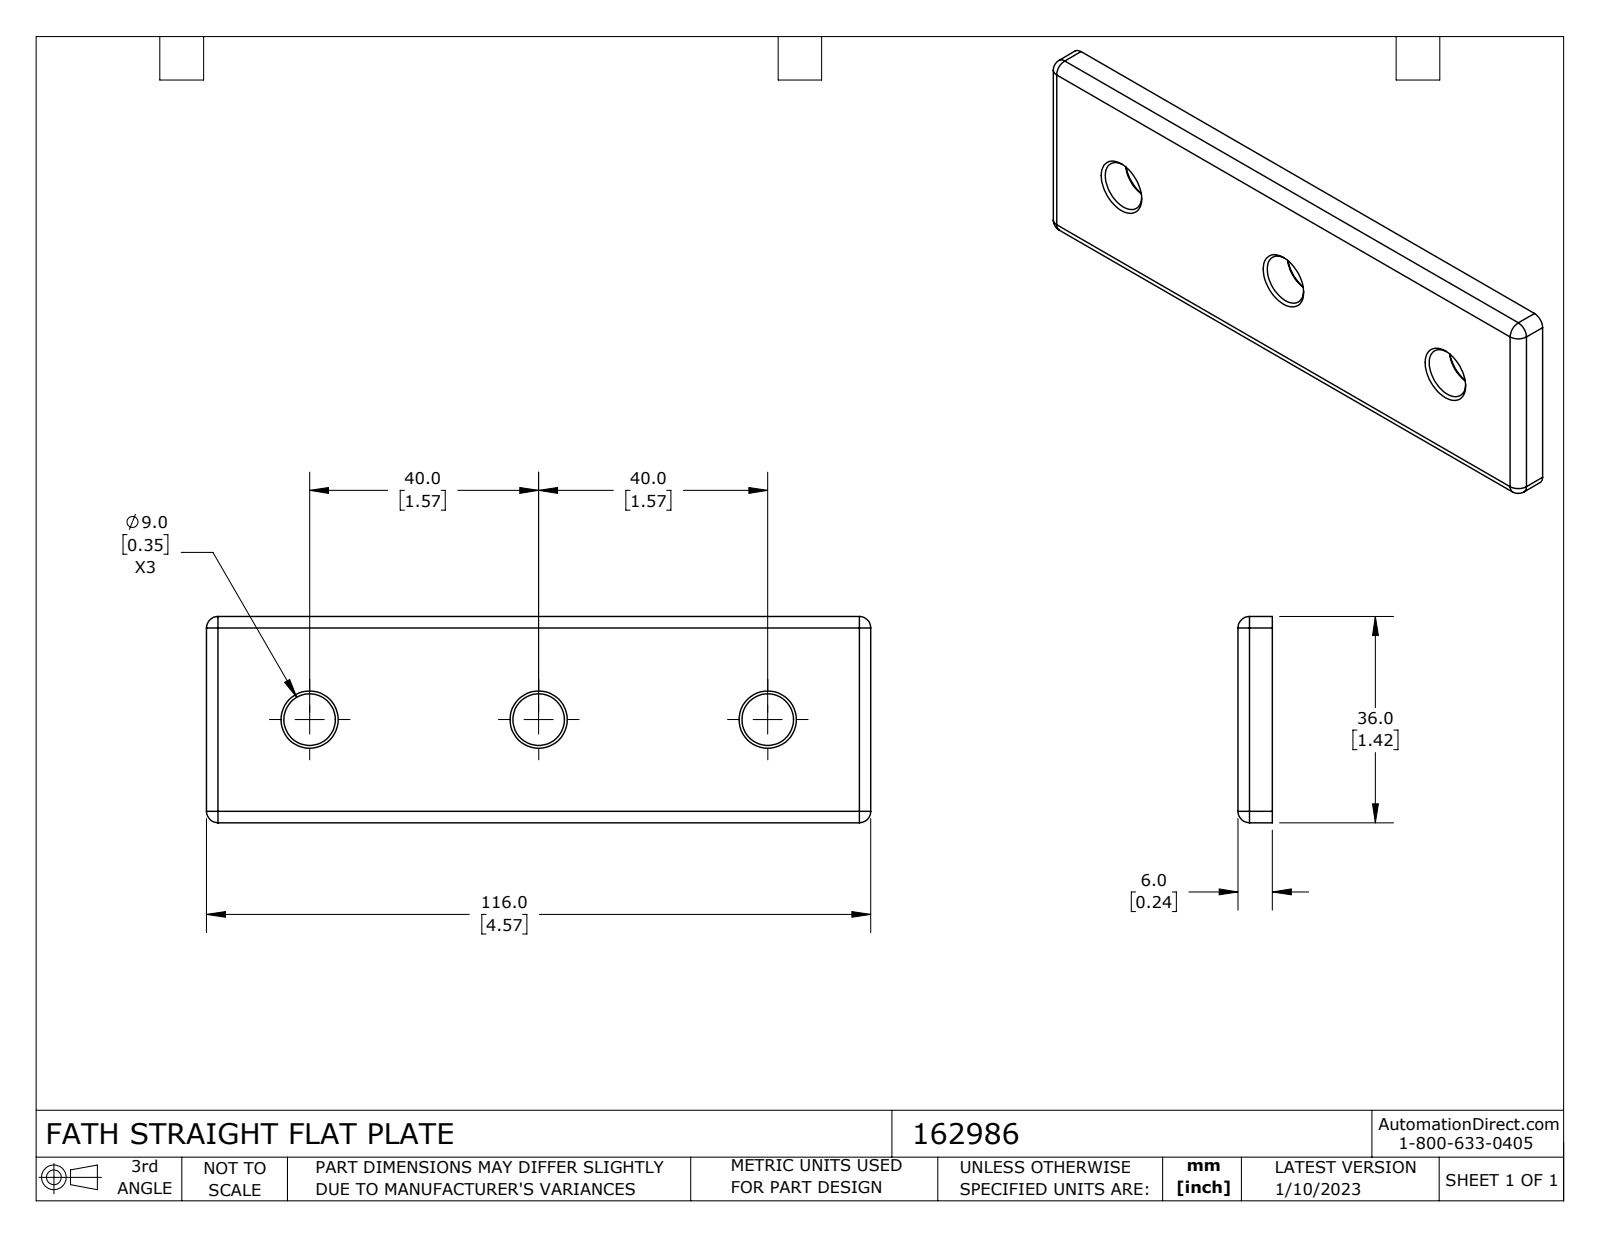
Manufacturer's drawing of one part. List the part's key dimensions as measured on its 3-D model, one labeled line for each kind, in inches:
Part name (STEP PRODUCT): 162986
STEP written by: SolidWorks 2021 (CONFIG_CONTROL_DESIGN)
Units: inches
Bodies: 1 solid, 36 faces (6 planar, 14 cylindrical, 16 other)
Overall size (bounding box): 4.567 × 1.417 × 0.236
Volume: 1.441 in³ · Surface area: 15.45 in²
Round holes (diameter × count): ⌀0.354 ×3
Partial cylindrical surfaces — rounded edges, fillets, slot ends (radius × count): R0.079 ×8
Main face-to-face distances: 0.236, 1.417, 4.567
Hole centre spacings: 1.575, 3.15
